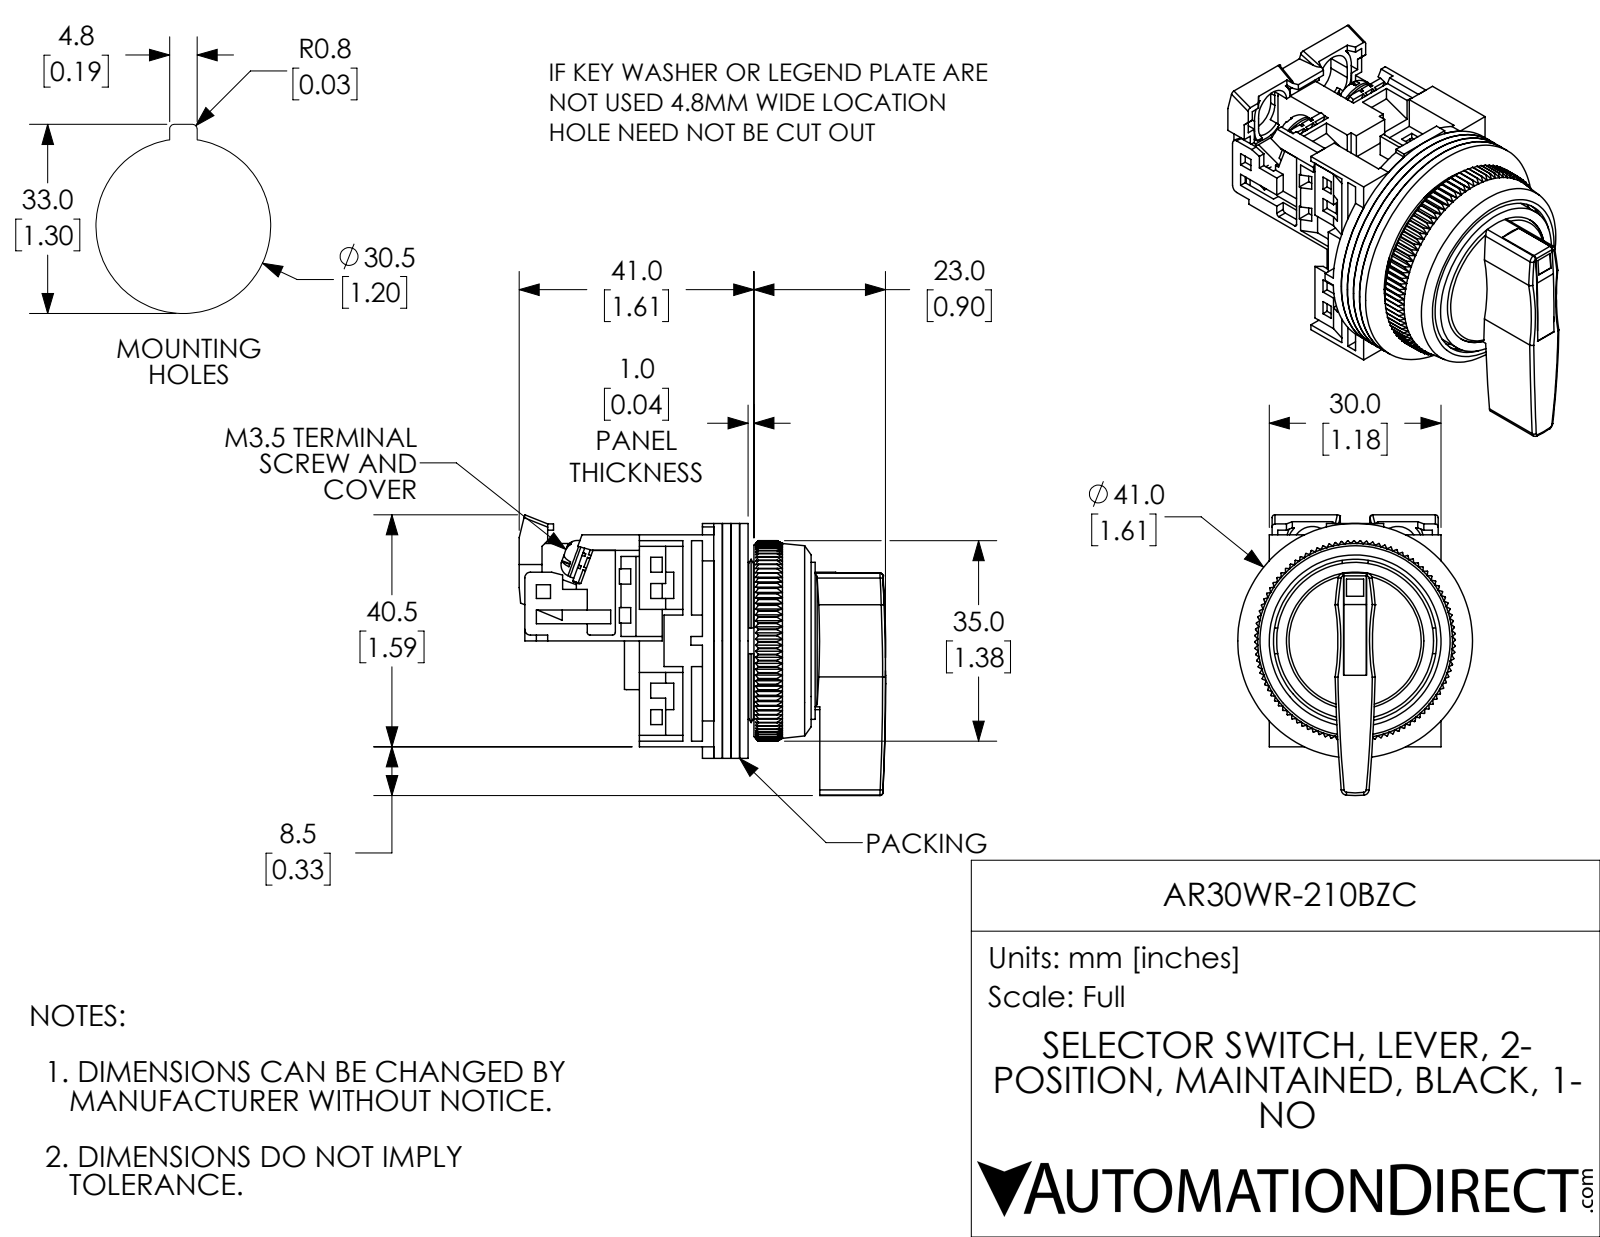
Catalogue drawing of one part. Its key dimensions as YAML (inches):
part_name: "AR30WR-210BZC"
step_written_by: "SolidWorks 2017 (AUTOMOTIVE_DESIGN)"
units: inches
bodies: {solids: 18, faces: 1374, planar: 901, cylindrical: 246, other: 227}
overall_size: [2.52, 1.929, 1.614]
volume: 1.857
surface_area: 53.45
round_holes:
  - {diameter: 0.138, count: 4}
  - {diameter: 0.142, count: 2}
  - {diameter: 0.118, count: 1}
  - {diameter: 0.315, count: 1}
  - {diameter: 0.472, count: 1}
  - {diameter: 0.48, count: 1}
  - {diameter: 0.512, count: 1}
  - {diameter: 0.819, count: 1}
  - {diameter: 0.945, count: 1}
  - {diameter: 1.122, count: 1}
  - {diameter: 1.181, count: 1}
  - {diameter: 1.252, count: 1}
round_bosses_or_shafts:
  - {diameter: 0.26, count: 2}
  - {diameter: 0.138, count: 2}
  - {diameter: 1.614, count: 1}
  - {diameter: 1.15, count: 1}
  - {diameter: 1.079, count: 1}
  - {diameter: 0.787, count: 1}
  - {diameter: 0.709, count: 1}
  - {diameter: 0.669, count: 1}
partial_cylinders:
  - {radius: 0.059, count: 8}
  - {radius: 0.02, count: 7}
  - {radius: 0.039, count: 6}
  - {radius: 0.138, count: 2}
  - {radius: 0.177, count: 2}
  - {radius: 1.575, count: 2}
  - {radius: 1.638, count: 2}
  - {radius: 2.89, count: 2}
face_to_face_distances: [0.059, 0.118, 0.177, 0.079, 0.039, 0.197, 0.512, 0.213, 0.256, 0.138]
hole_center_spacings: [0.579, 0.61]
